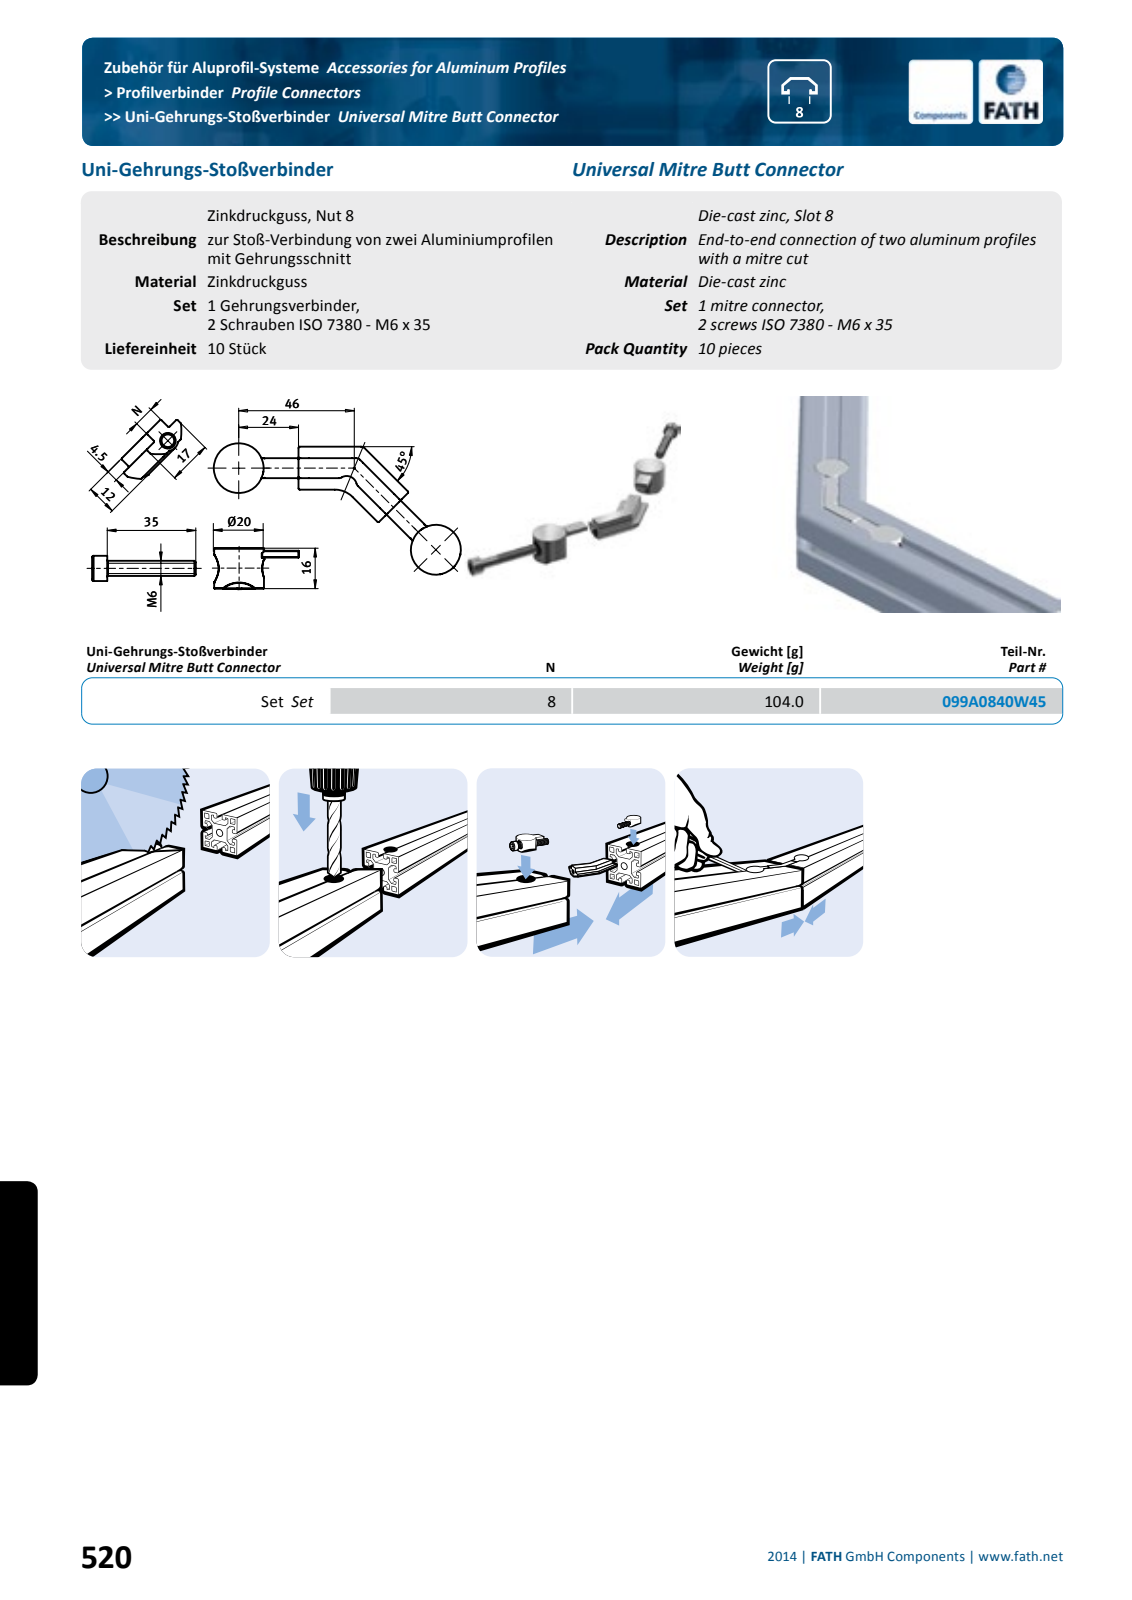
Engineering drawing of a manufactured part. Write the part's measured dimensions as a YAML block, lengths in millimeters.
part_name: "fath_099a0840w45_1; fath_099a0840w45_2; fath_099a0840w45_3; fath_099a0840w45_4 (+1 more)"
step_written_by: "Spatial InterOp 3D (automotive_design)"
units: millimeters
bodies: {solids: 5, faces: 567, planar: 90, cylindrical: 177, other: 300}
overall_size: [99.34, 52.69, 16.2]
volume: 14584
surface_area: 10183
round_holes:
  - {diameter: 5, count: 2}
  - {diameter: 6.6, count: 2}
  - {diameter: 14.2, count: 2}
round_bosses_or_shafts:
  - {diameter: 19.7, count: 2}
  - {diameter: 10, count: 2}
  - {diameter: 6, count: 2}
partial_cylinders:
  - {radius: 0.5, count: 38}
  - {radius: 2, count: 4}
  - {radius: 24.5, count: 4}
  - {radius: 4, count: 3}
  - {radius: 10, count: 1}
face_to_face_distances: [16, 11.48, 4.52, 15.98, 4.5, 1, 12.3, 0.82, 3.68, 3.7]
